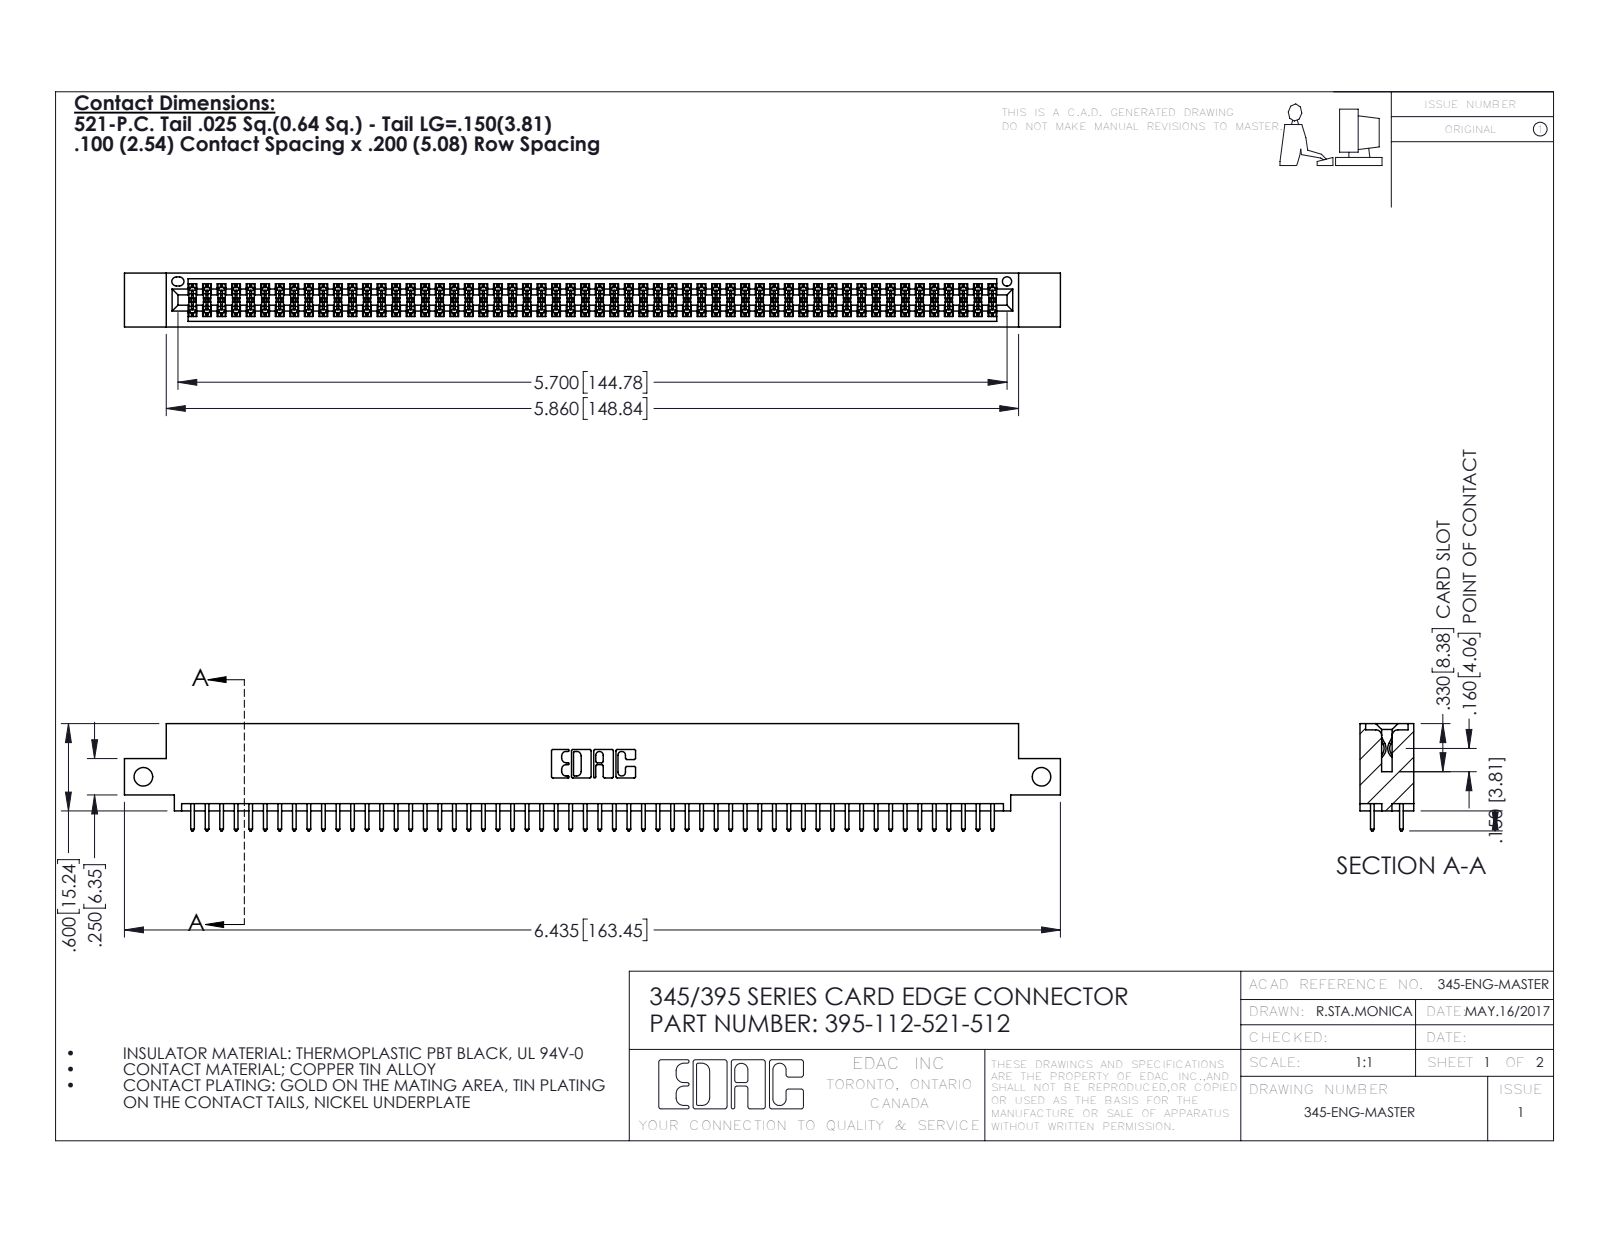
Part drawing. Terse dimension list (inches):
name: 345-292-001_345-293-121; 345 Part_0.110 Offset - Side Mount; 395-112-521-512
written by: SolidWorks 2016 (CONFIG_CONTROL_DESIGN)
unit: in
bodies: 113 solids, 5730 faces (3780 planar, 1950 cylindrical, 0 other)
size: 6.435 × 0.737 × 0.37
volume: 0.964 in³; area: 36.1 in²
holes: 2× ⌀0.128, 1× ⌀0.064
rounds: 168× R0.006, 112× R0.01, 22× R0.01, 6× R0.007, 6× R0.031, 3× R0.026, 2× R0.014, 2× R0.019
face distances: 0.072, 0.298, 0.2, 0.098, 0.272, 0.025, 0.37, 0.225, 0.175, 0.149
hole spacings: 6.175
